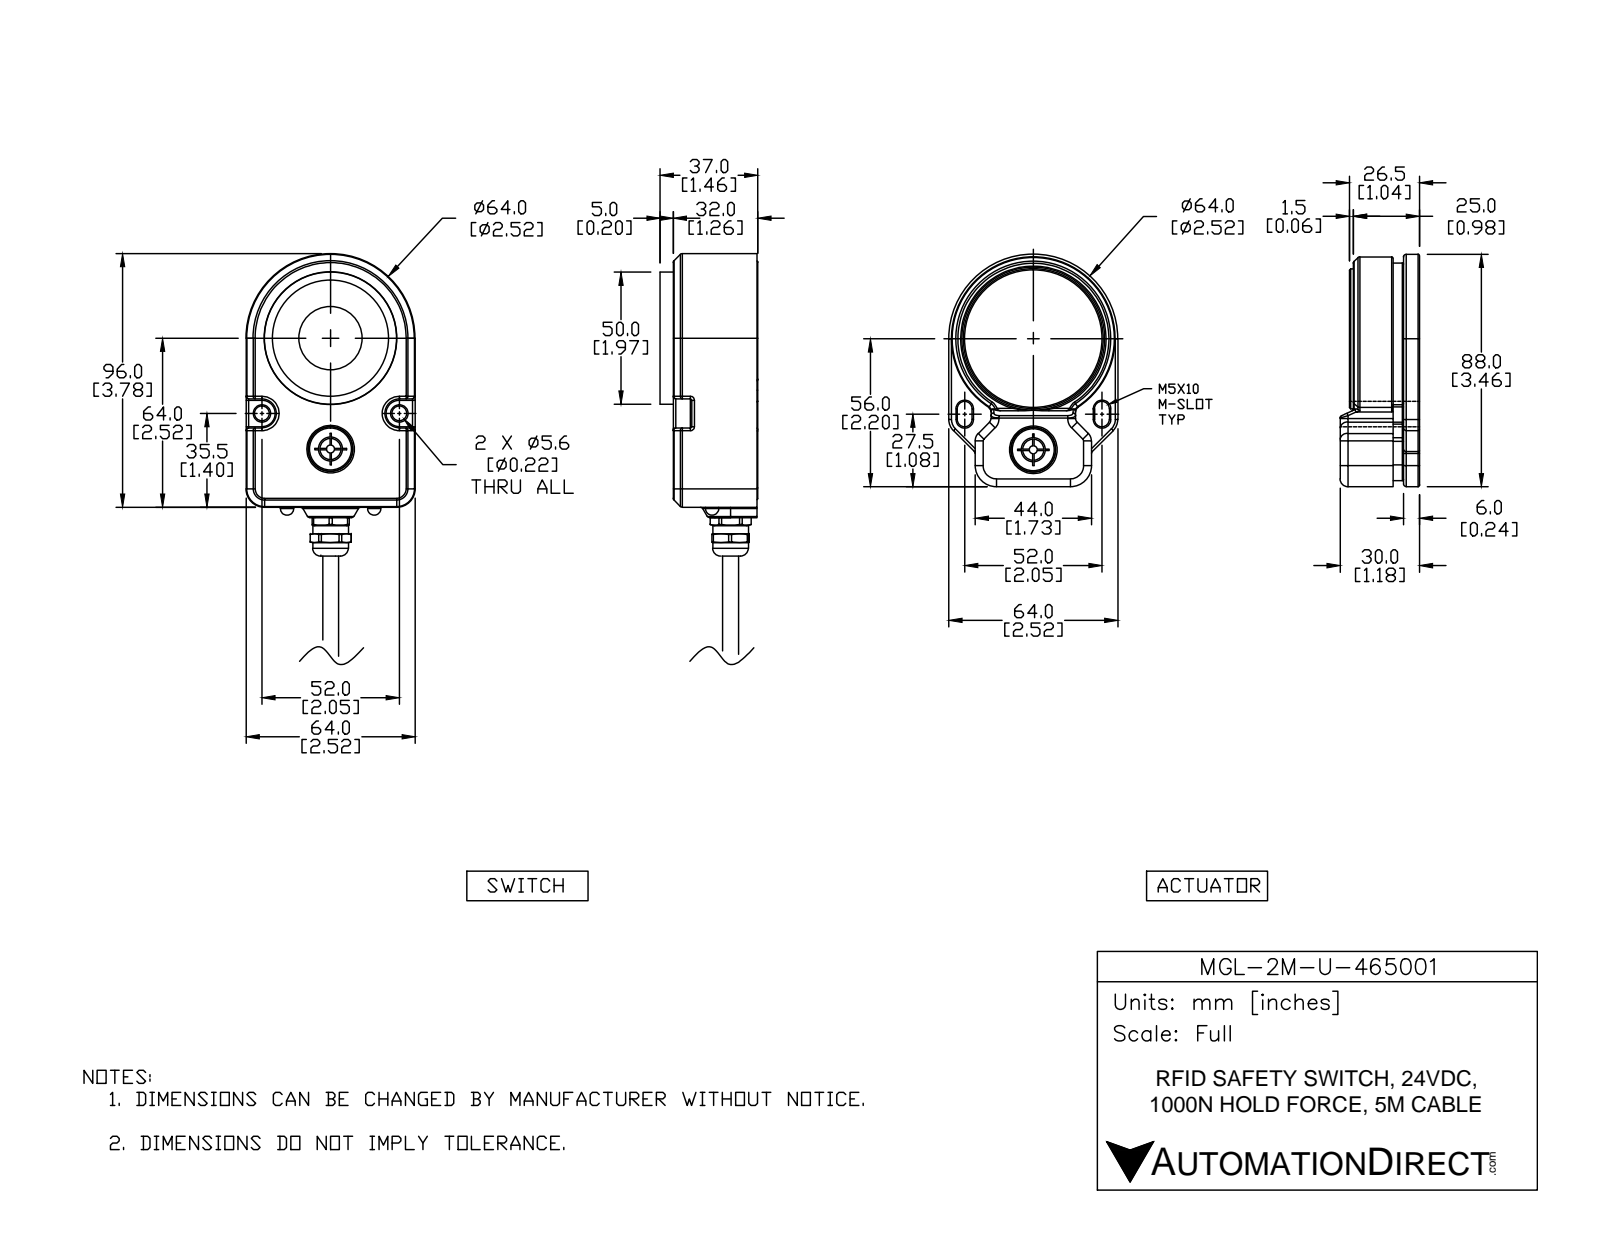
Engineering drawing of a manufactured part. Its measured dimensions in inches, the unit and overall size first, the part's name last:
Units: inches
Overall size (bounding box): 7.717 × 2.539 × 2.52
Round holes (diameter × count): ⌀0.098 ×8, ⌀0.157 ×8, ⌀0.13 ×6, ⌀0.315 ×6, ⌀0.197 ×5, ⌀0.323 ×3, ⌀0.22 ×2, ⌀0.354 ×2, ⌀0.374 ×2, ⌀0.413 ×2, ⌀0.669 ×2, ⌀0.252 ×1
Round bosses / shafts (diameter × count): ⌀0.02 ×4, ⌀0.079 ×3, ⌀0.236 ×2, ⌀0.228 ×2, ⌀0.213 ×2, ⌀2.441 ×1, ⌀2.26 ×1, ⌀2.087 ×1
Partial cylindrical surfaces — rounded edges, fillets, slot ends (radius × count): R0.02 ×216, R0.039 ×87, R0.079 ×30, R0.012 ×17, R0.118 ×15, R0.157 ×9, R0.024 ×7, R0.177 ×6
Main face-to-face distances: 0.236, 0.413, 0.118, 0.748, 1.89, 2.303, 1.043, 0.394, 0.354, 1.142
Hole centre spacings: 0.706, 0.768, 1.086, 1.024, 0.346, 0.376, 0.382, 0.384
Volume: 12.42 in³ · Surface area: 169.6 in²
Bodies: 20 solids, 1852 faces (454 planar, 786 cylindrical, 612 other)
Part name (STEP PRODUCT): MGL-2M-U-465001_2; MGL-2M-U-465001; MGL-2M-U-465001_1
STEP written by: SolidWorks 2017 (AUTOMOTIVE_DESIGN)
